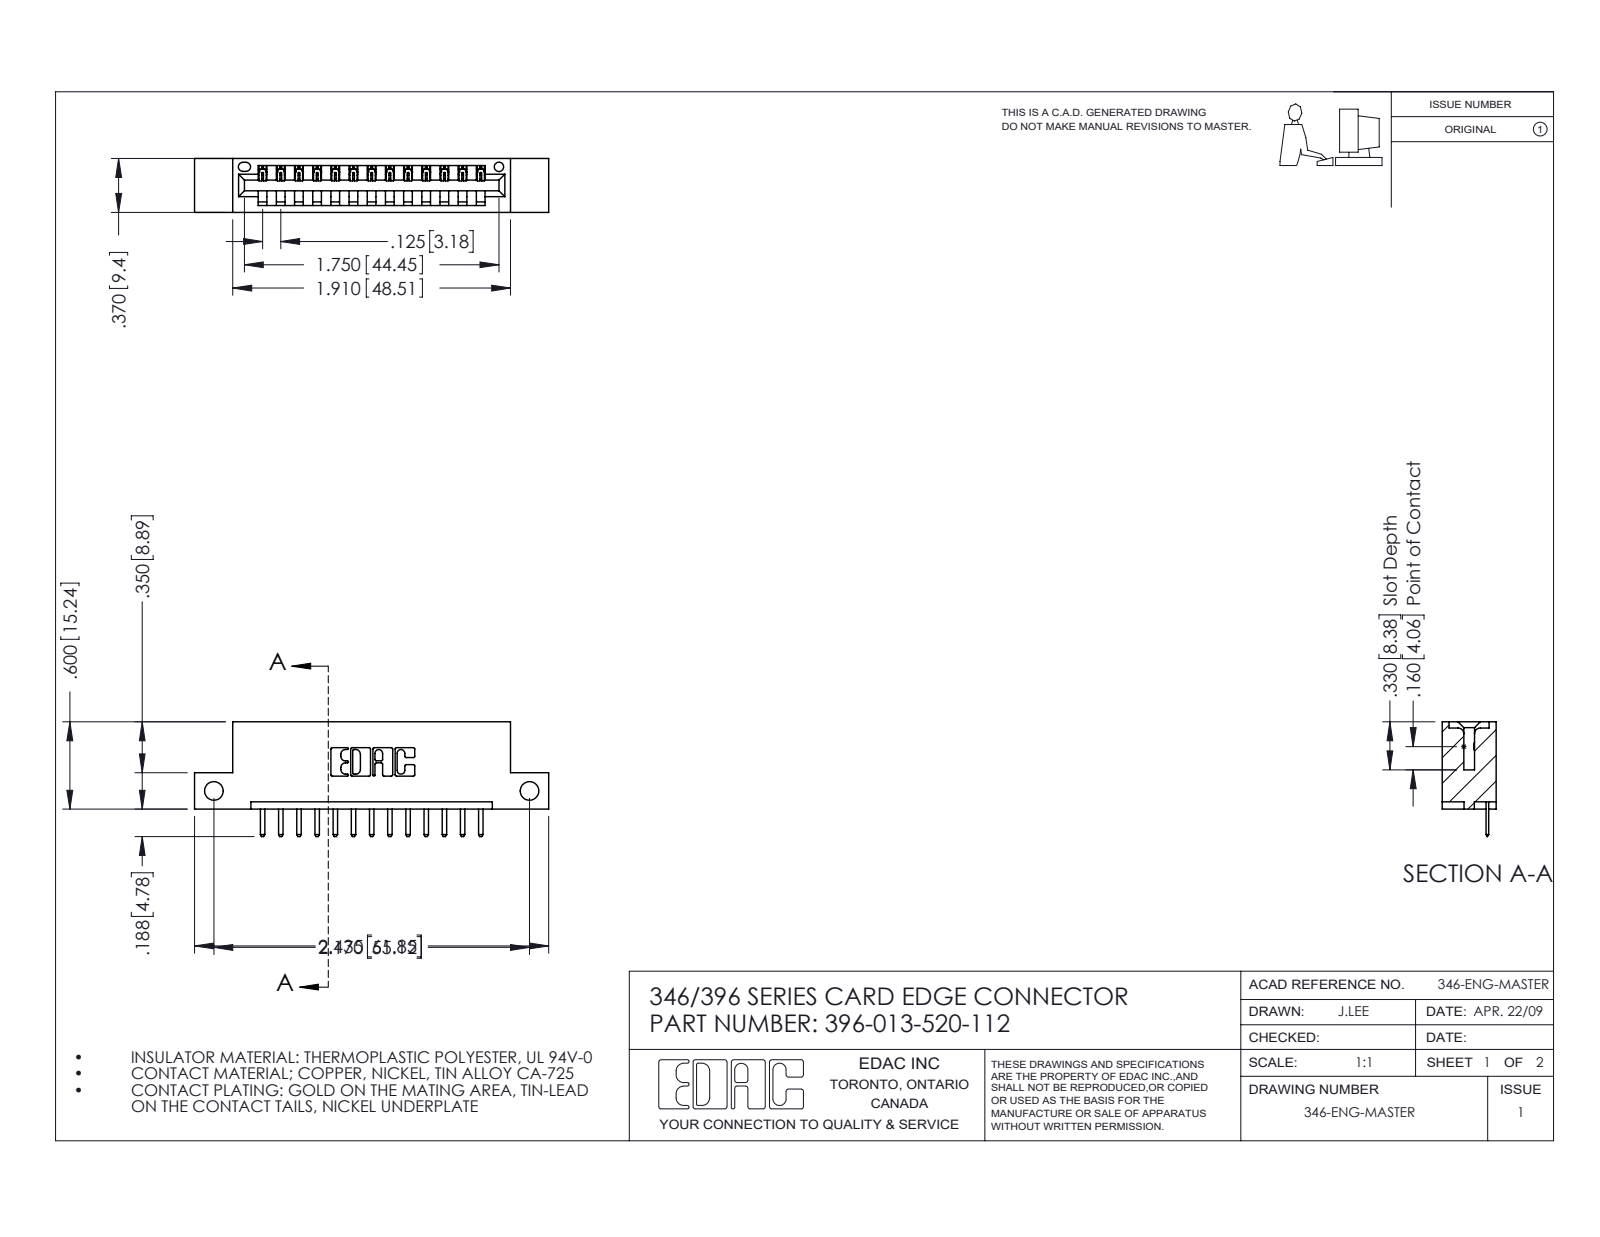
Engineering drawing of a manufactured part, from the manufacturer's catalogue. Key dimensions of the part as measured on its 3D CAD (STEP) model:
Part name (STEP PRODUCT): 396-013-520-112; 346 Part_Flush Mounting Lugs - Side Mount; 345-292-001_345-293-120
STEP written by: SolidWorks 2016 (CONFIG_CONTROL_DESIGN)
Units: inches
Bodies: 14 solids, 928 faces (622 planar, 306 cylindrical, 0 other)
Overall size (bounding box): 2.435 × 0.788 × 0.37
Volume: 0.341 in³ · Surface area: 9.936 in²
Round holes (diameter × count): ⌀0.128 ×2, ⌀0.064 ×1
Partial cylindrical surfaces — rounded edges, fillets, slot ends (radius × count): R0.01 ×28, R0.006 ×26, R0.01 ×22, R0.007 ×6, R0.031 ×6, R0.026 ×3, R0.031 ×2, R0.04 ×2
Main face-to-face distances: 0.25, 0.37, 0.048, 0.322, 0.148, 0.222, 0.1, 0.174, 0.072, 0.298
Hole centre spacings: 2.17
